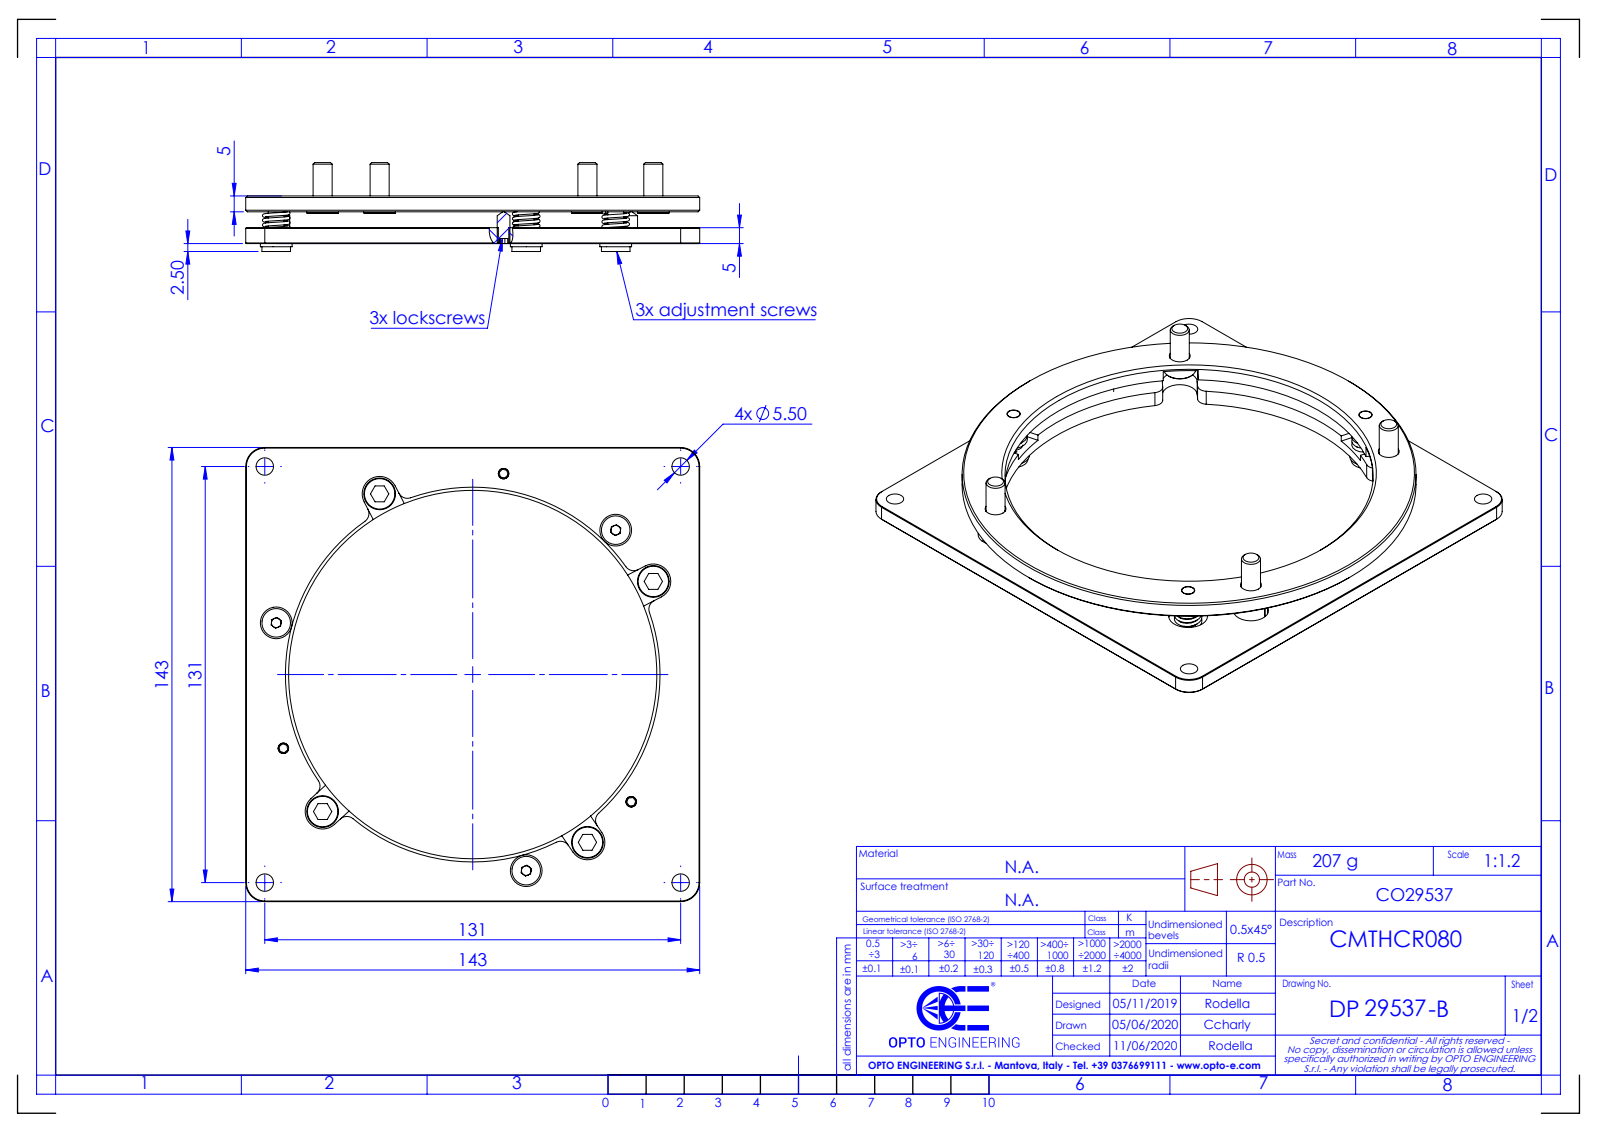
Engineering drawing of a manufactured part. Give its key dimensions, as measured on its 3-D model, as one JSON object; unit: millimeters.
{"part_name": "DP29537", "step_written_by": "SolidWorks 2021 (CONFIG_CONTROL_DESIGN)", "units": "millimeters", "bodies": {"solids": 0, "faces": 272, "planar": 115, "cylindrical": 103, "other": 54}, "overall_size": [143, 143, 28], "round_holes": [[5.5, 4], [6.6, 4], [4.2, 3], [3.3, 1], [116, 1], [118, 1]], "round_bosses_or_shafts": [[10, 7], [6, 4], [9, 3], [5, 3], [4, 3], [143, 1]], "partial_cylinders_radius": [[3, 8], [5.5, 4], [6, 4], [6.1, 3]], "face_to_face_distances": [5, 10, 15, 143, 10.5, 1.5, 12, 16, 4, 5.5], "hole_center_spacings": [64, 92.63, 131, 37.19, 63.99, 95.21, 110.85, 125.21]}
